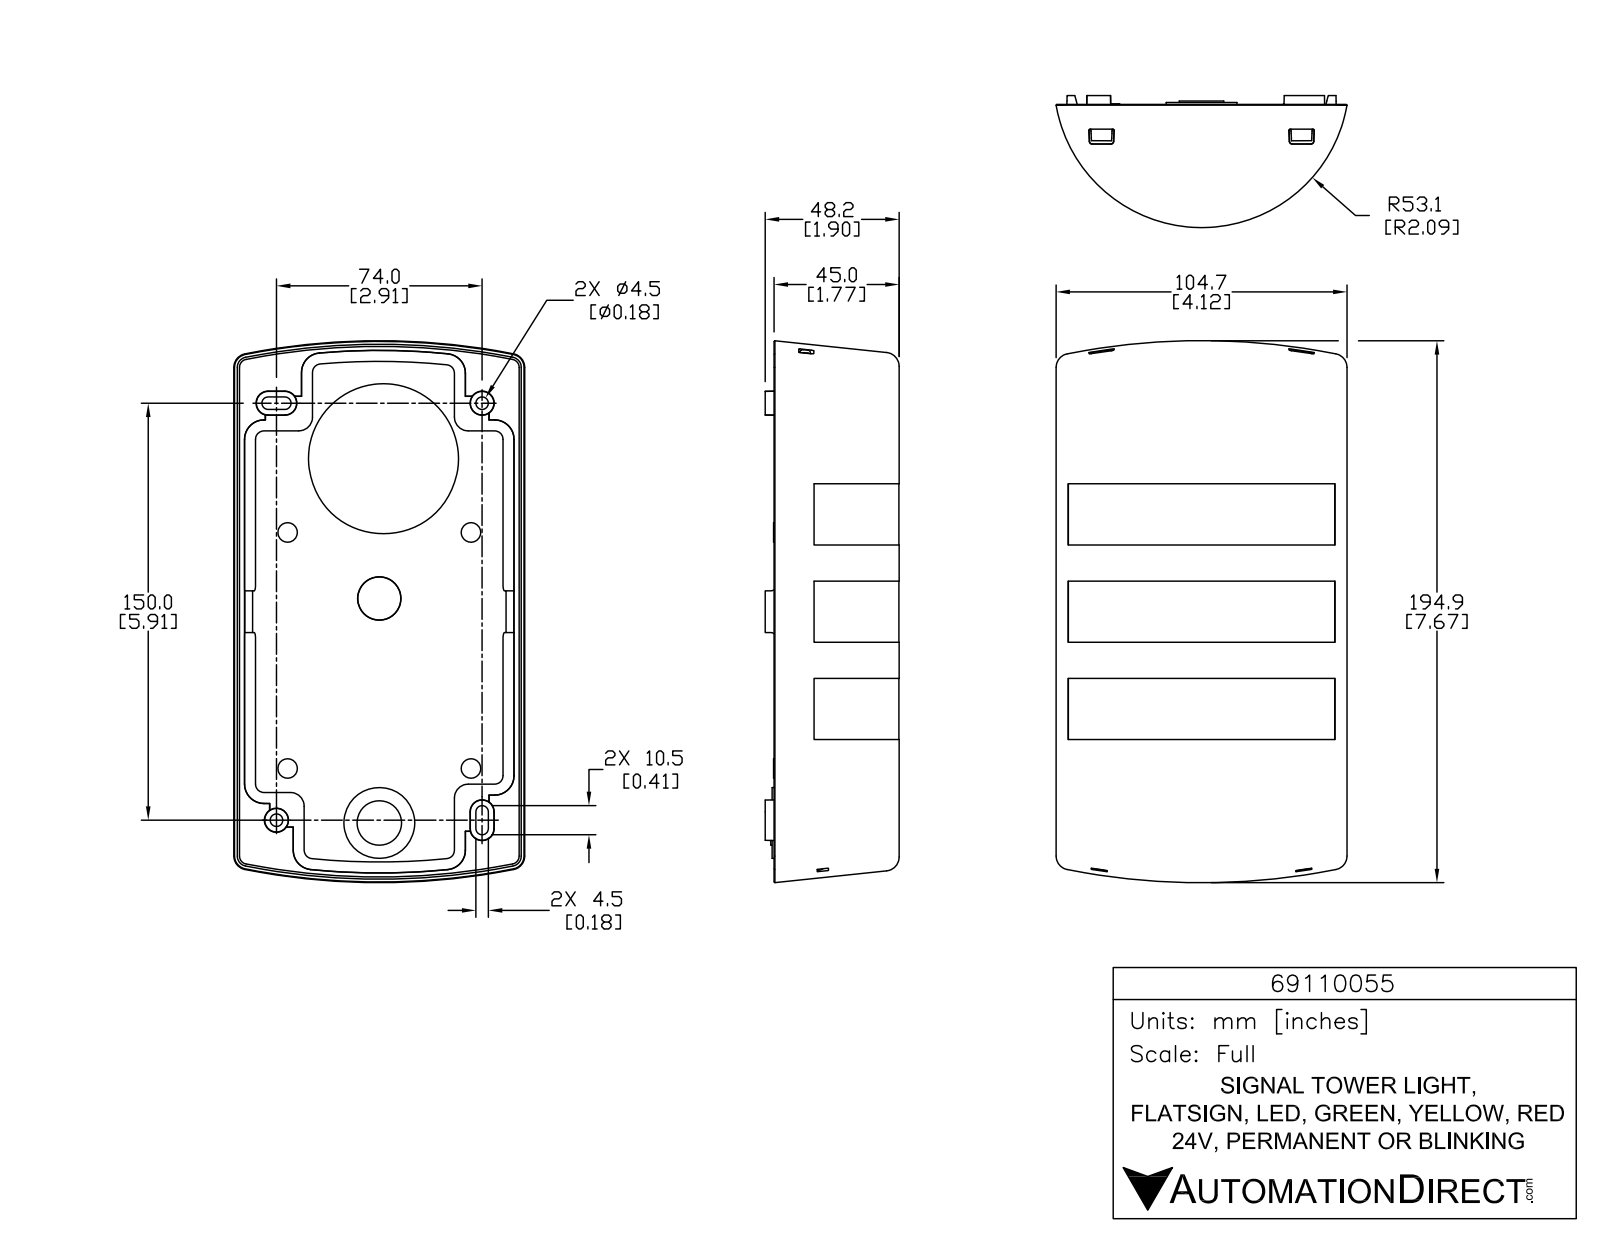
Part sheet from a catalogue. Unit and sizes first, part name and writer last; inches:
Units: inches
Overall size (bounding box): 7.675 × 4.122 × 1.901
Round holes (diameter × count): ⌀0.089 ×1
Round bosses / shafts (diameter × count): ⌀2.126 ×1, ⌀1.004 ×1, ⌀0.63 ×1, ⌀0.514 ×1, ⌀0.128 ×1
Partial cylindrical surfaces — rounded edges, fillets, slot ends (radius × count): R0.039 ×12, R0.012 ×4, R0.008 ×3, R0.008 ×2, R0.018 ×2, R0.019 ×2, R0.019 ×2, R0.02 ×2
Main face-to-face distances: 0.031, 0.079, 0.047, 0.11, 0.063, 0.157, 0.039, 0.02, 0.138, 0.118
Volume: 38.36 in³ · Surface area: 92.69 in²
Bodies: 1 solid, 1074 faces (520 planar, 128 cylindrical, 426 other)
Part name (STEP PRODUCT): 69110055
STEP written by: SolidWorks 2017 (AUTOMOTIVE_DESIGN)
